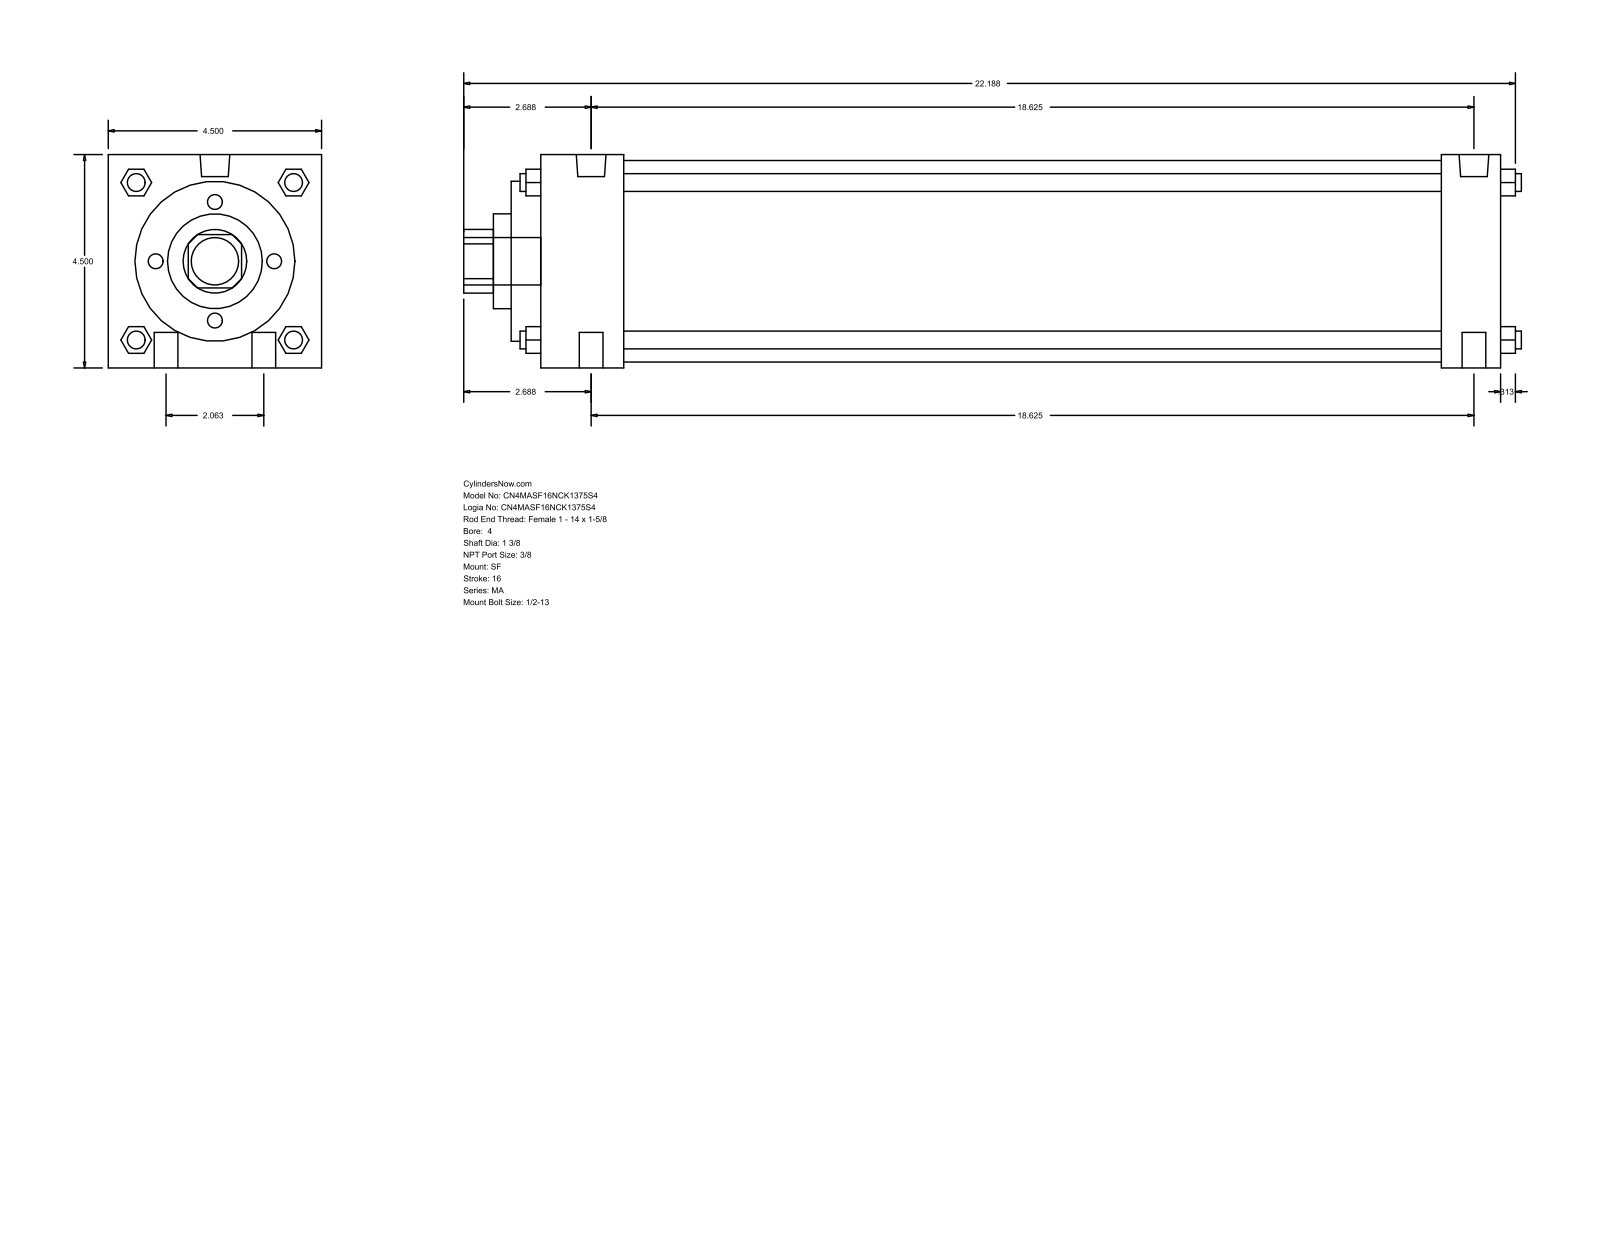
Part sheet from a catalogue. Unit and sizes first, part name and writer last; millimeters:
Units: millimetres
Overall size (bounding box): 566.74 × 114.3 × 114.3
Round holes (diameter × count): ⌀34.92 ×1, ⌀50.8 ×1, ⌀85.72 ×1, ⌀107.95 ×1
Round bosses / shafts (diameter × count): ⌀12.7 ×4, ⌀9.53 ×4, ⌀15.93 ×2, ⌀11.11 ×2, ⌀25.4 ×1
Partial cylindrical surfaces — rounded edges, fillets, slot ends (radius × count): R17.06 ×1
Main face-to-face distances: 114.3, 514.35, 530.22, 15.87, 498.48, 482.61, 31.74, 60.32, 44.45, 438.16
Bodies: 0 solids, 126 faces (95 planar, 31 cylindrical, 0 other)
Part name (STEP PRODUCT): MA_SF__0400_1.375
STEP written by: GSSL Pune (CONFIG_CONTROL_DESIGN)
